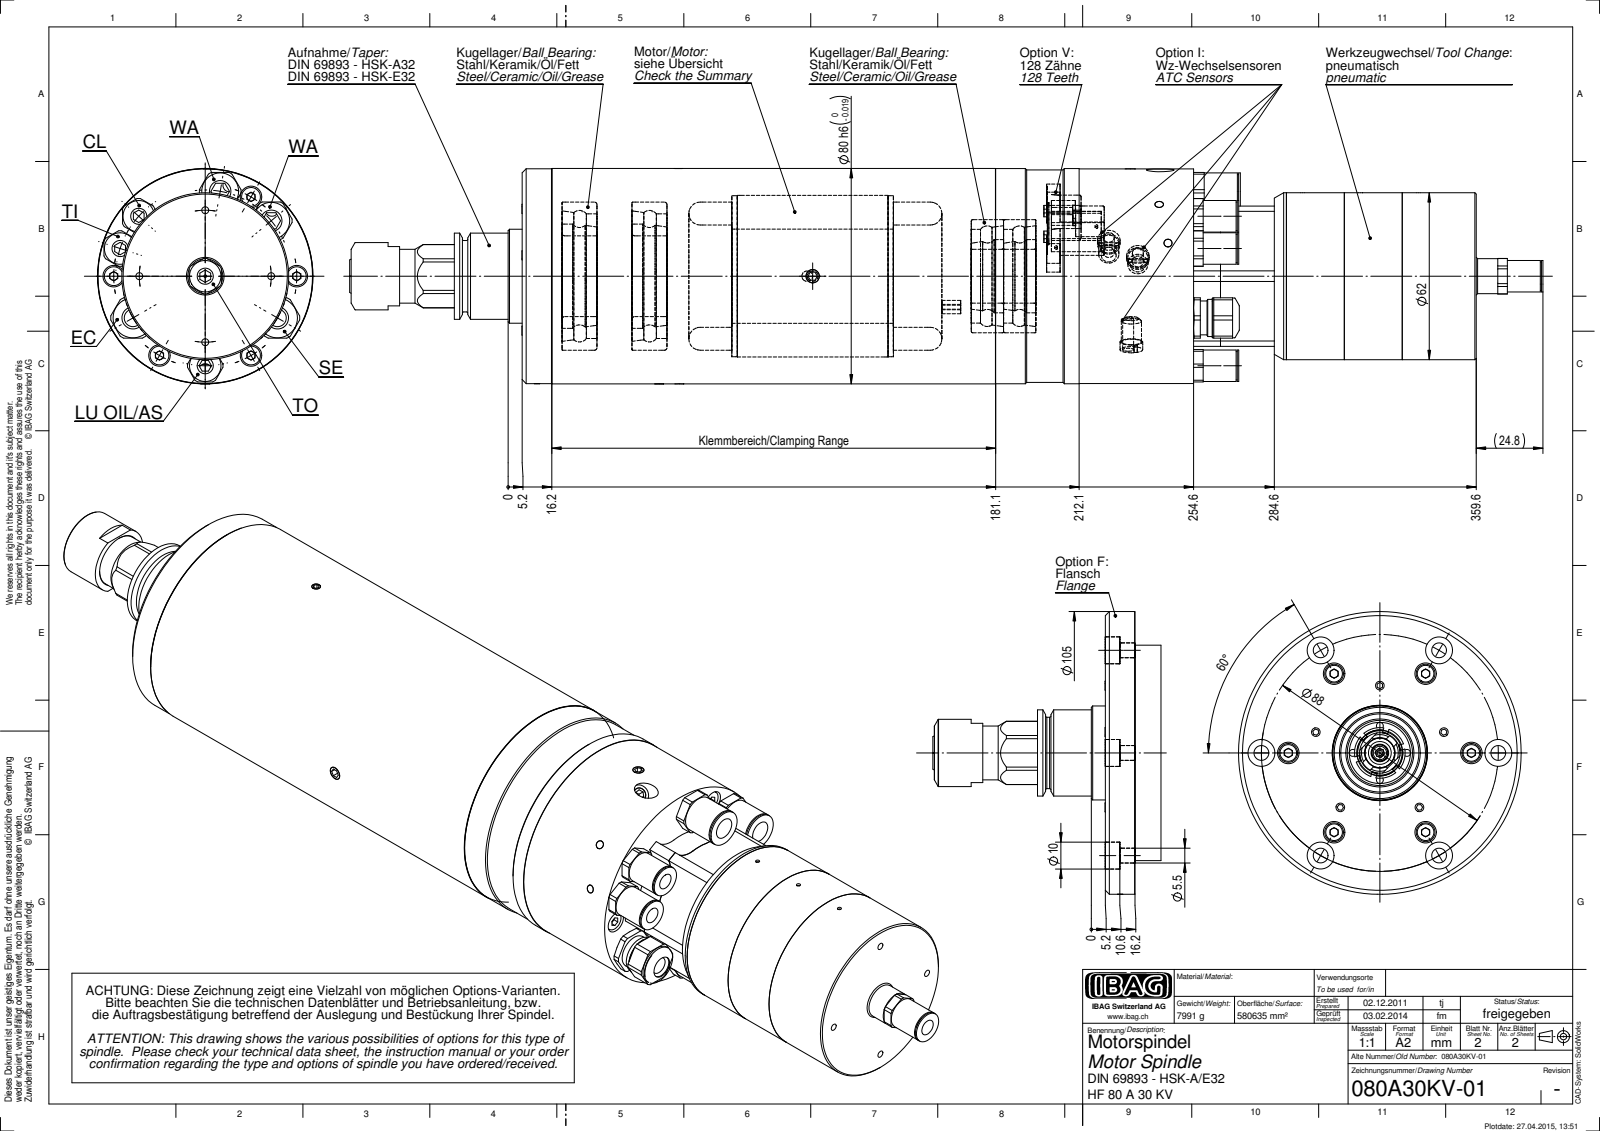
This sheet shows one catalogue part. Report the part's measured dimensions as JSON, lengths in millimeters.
{"part_name": "080A30KV-01", "step_written_by": "SolidWorks 2012 (CONFIG_CONTROL_DESIGN)", "units": "millimeters", "bodies": {"solids": 0, "faces": 708, "planar": 288, "cylindrical": 284, "other": 136}, "overall_size": [443.24, 80, 80], "round_holes": [[8, 8], [2.6, 4], [6, 4], [1.5, 3], [3.3, 3], [4.5, 3], [12.5, 3], [5, 2], [6.5, 2], [8.2, 2], [7.3, 1], [10, 1]], "round_bosses_or_shafts": [[11.7, 4], [7, 4], [14.8, 2], [13.79, 2], [13.7, 2], [12.59, 2], [80, 1], [79.9, 1]], "partial_cylinders_radius": [[9.5, 12], [6.6, 4], [7.75, 2], [8.25, 2], [11.75, 1], [22.4, 1], [29, 1]], "face_to_face_distances": [354.4, 249.4, 105, 206.9, 42.5, 147.5, 11, 195.9, 238.4, 343.4], "hole_center_spacings": [34, 17.07, 17.7, 24.5, 30.38, 34.65, 41.91, 46.01]}
